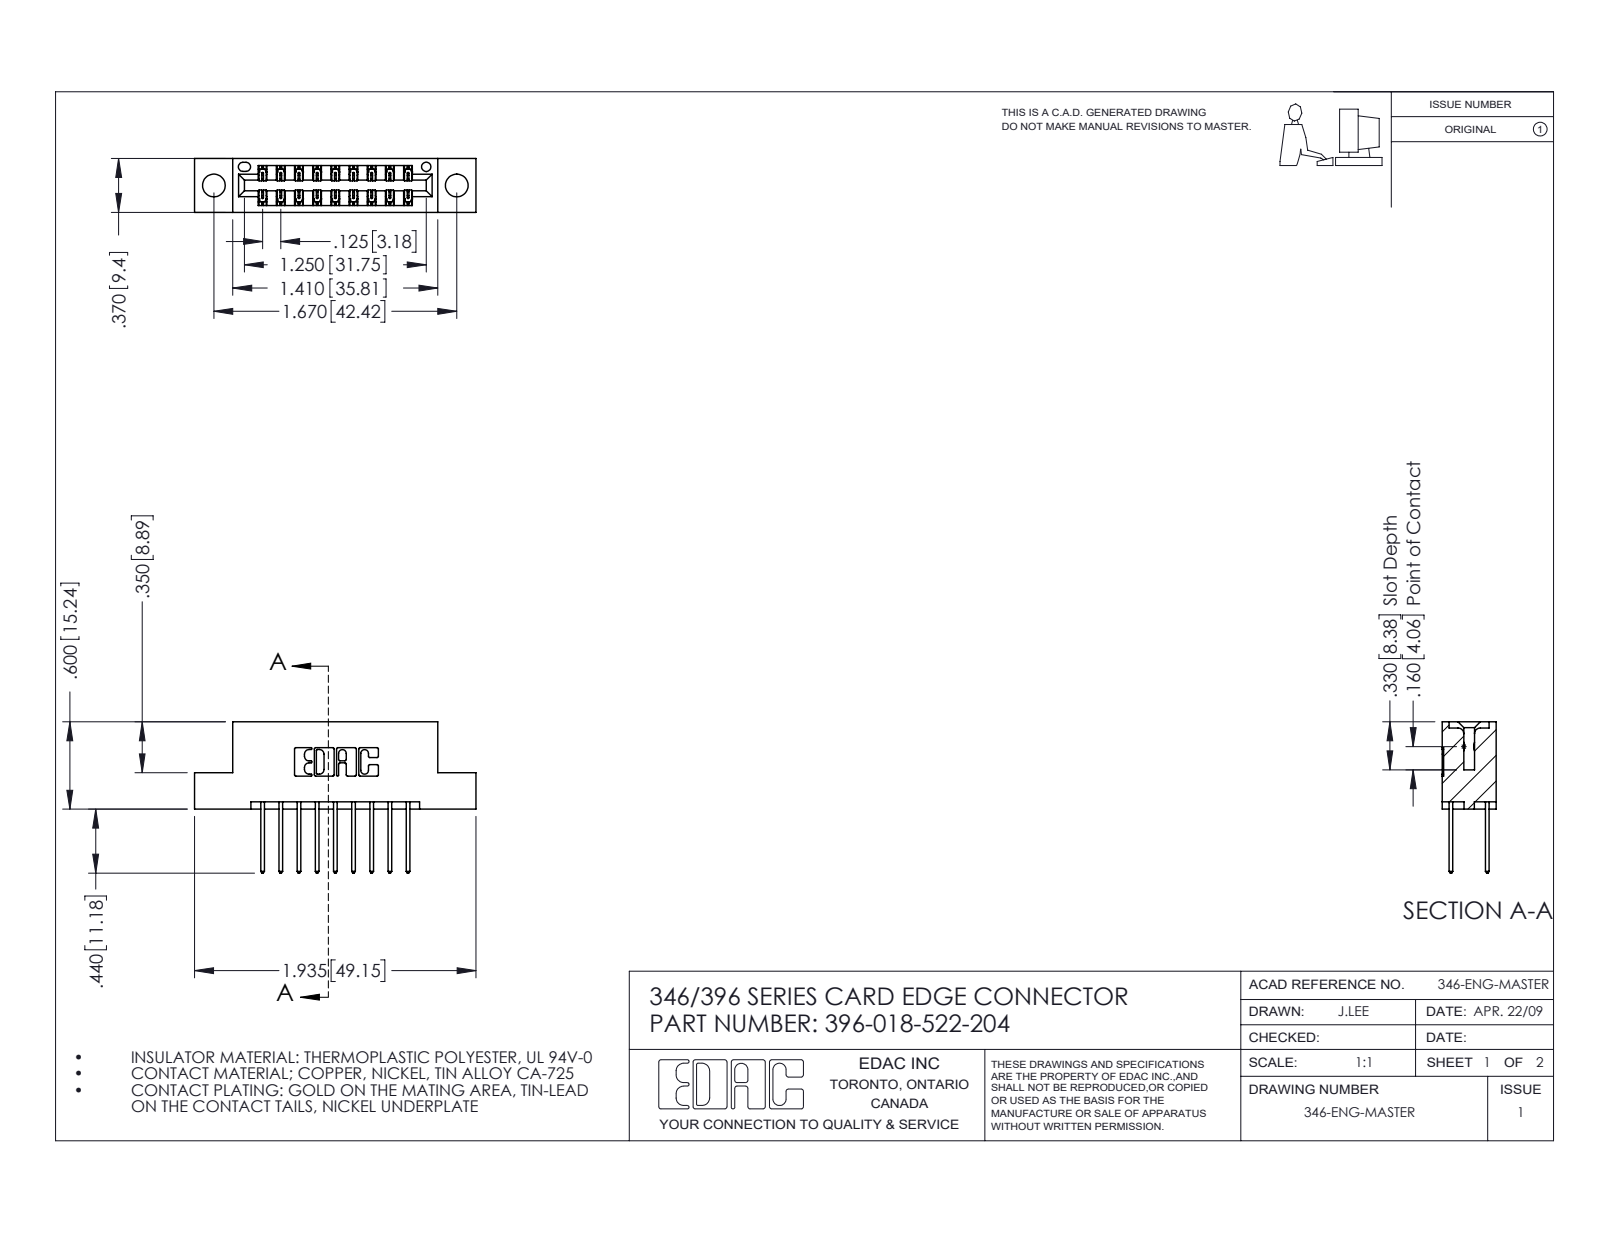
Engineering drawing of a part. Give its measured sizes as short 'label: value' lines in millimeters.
name: 396-018-522-204; 345-292-001_345-293-122; 346 Part_Flush Mounting Lugs - 0.156 Dia-TH
written by: SolidWorks 2016 (CONFIG_CONTROL_DESIGN)
unit: mm
bodies: 19 solids, 1058 faces (706 planar, 352 cylindrical, 0 other)
size: 49.1 × 26.4 × 9.4
volume: 4 490 mm³; area: 5 686 mm²
holes: 2× ⌀4, 1× ⌀1.6
rounds: 27× R0.2, 22× R0.3, 18× R0.3, 6× R0.2, 6× R0.8, 3× R0.7, 2× R0.4, 2× R0.6
face distances: 6.4, 1.2, 8.2, 9.4, 1.8, 7.6, 0.6, 7, 3.8, 5.6
hole spacings: 6.2, 37.2, 42.4
